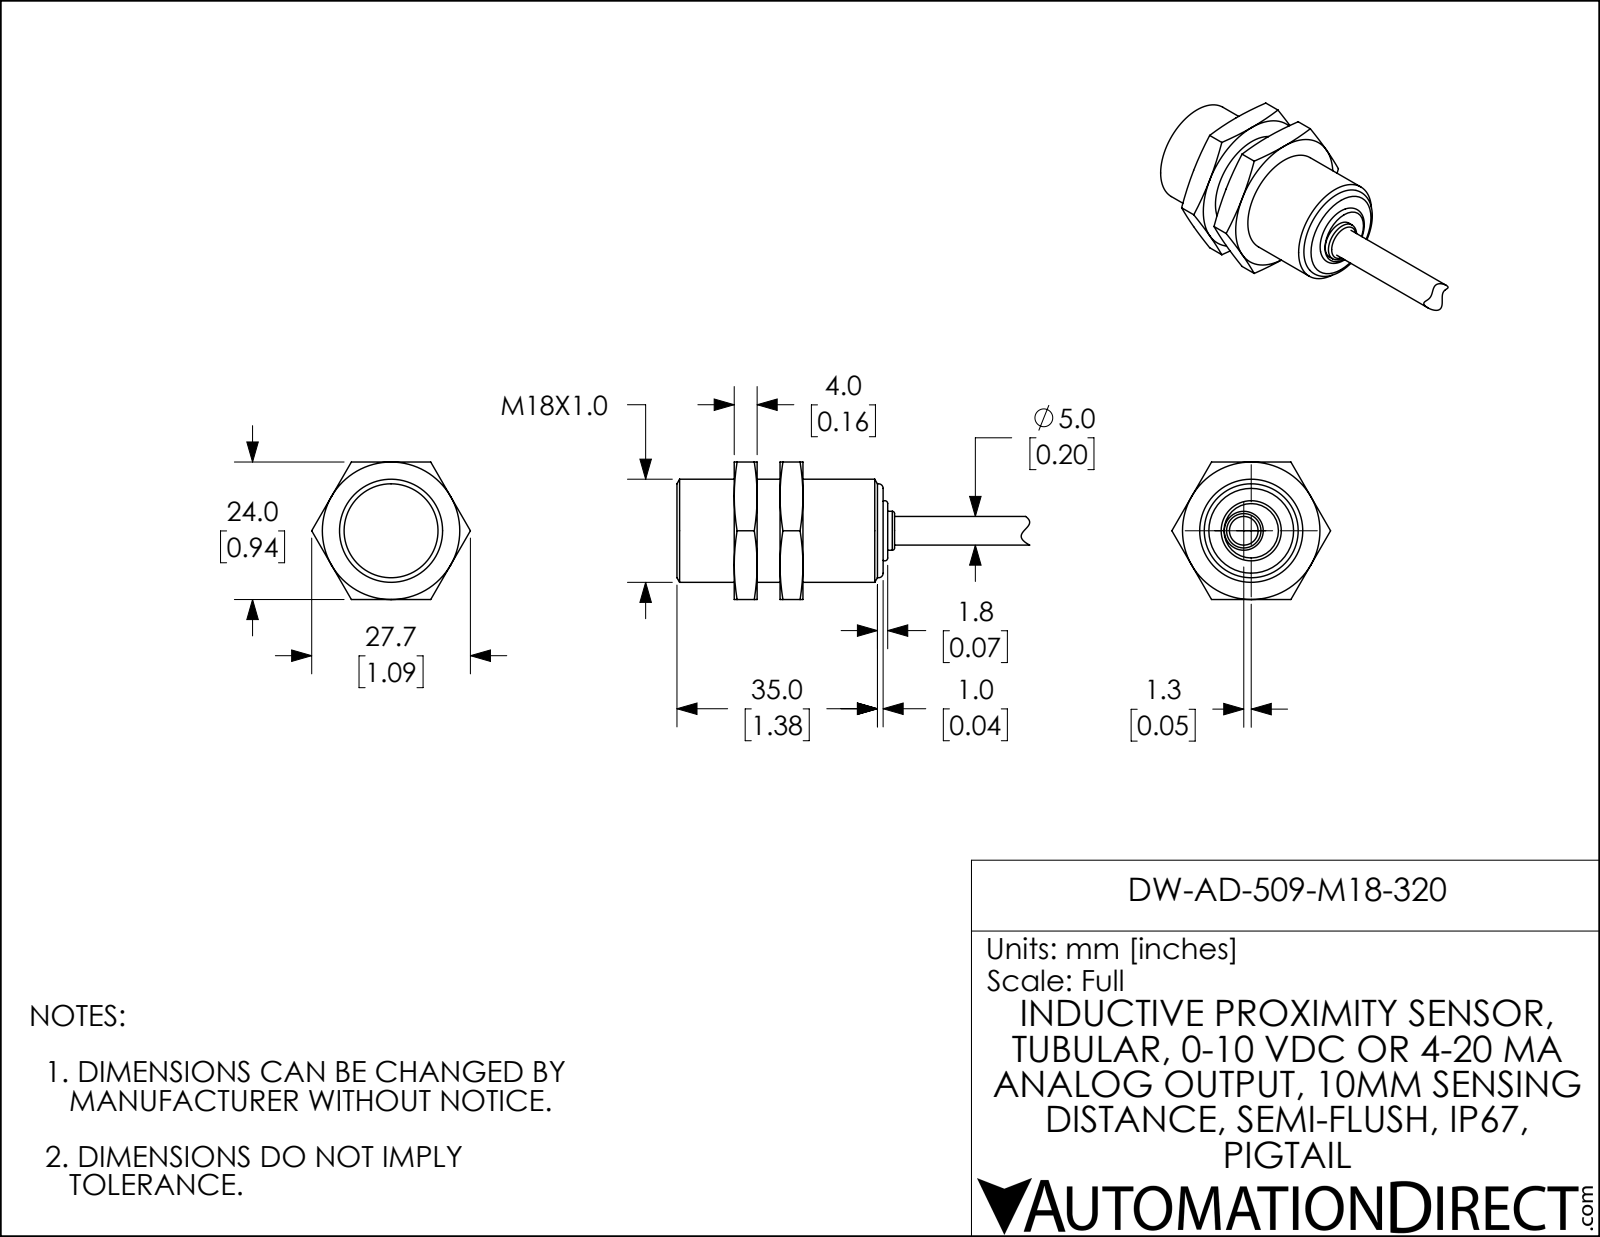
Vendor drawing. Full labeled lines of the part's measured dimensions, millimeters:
Part name (STEP PRODUCT): DW-AD-509-M18-320
STEP written by: SolidWorks 2018 (AUTOMOTIVE_DESIGN)
Units: millimetres
Bodies: 4 solids, 60 faces (21 planar, 5 cylindrical, 34 other)
Overall size (bounding box): 61.6 × 27.71 × 24
Volume: 11 879 mm³ · Surface area: 5 082 mm²
Round holes (diameter × count): ⌀16.92 ×1
Round bosses / shafts (diameter × count): ⌀18 ×1, ⌀6.8 ×1, ⌀5 ×1
Main face-to-face distances: 4, 8, 24, 14, 22, 18, 10, 12, 36, 26
